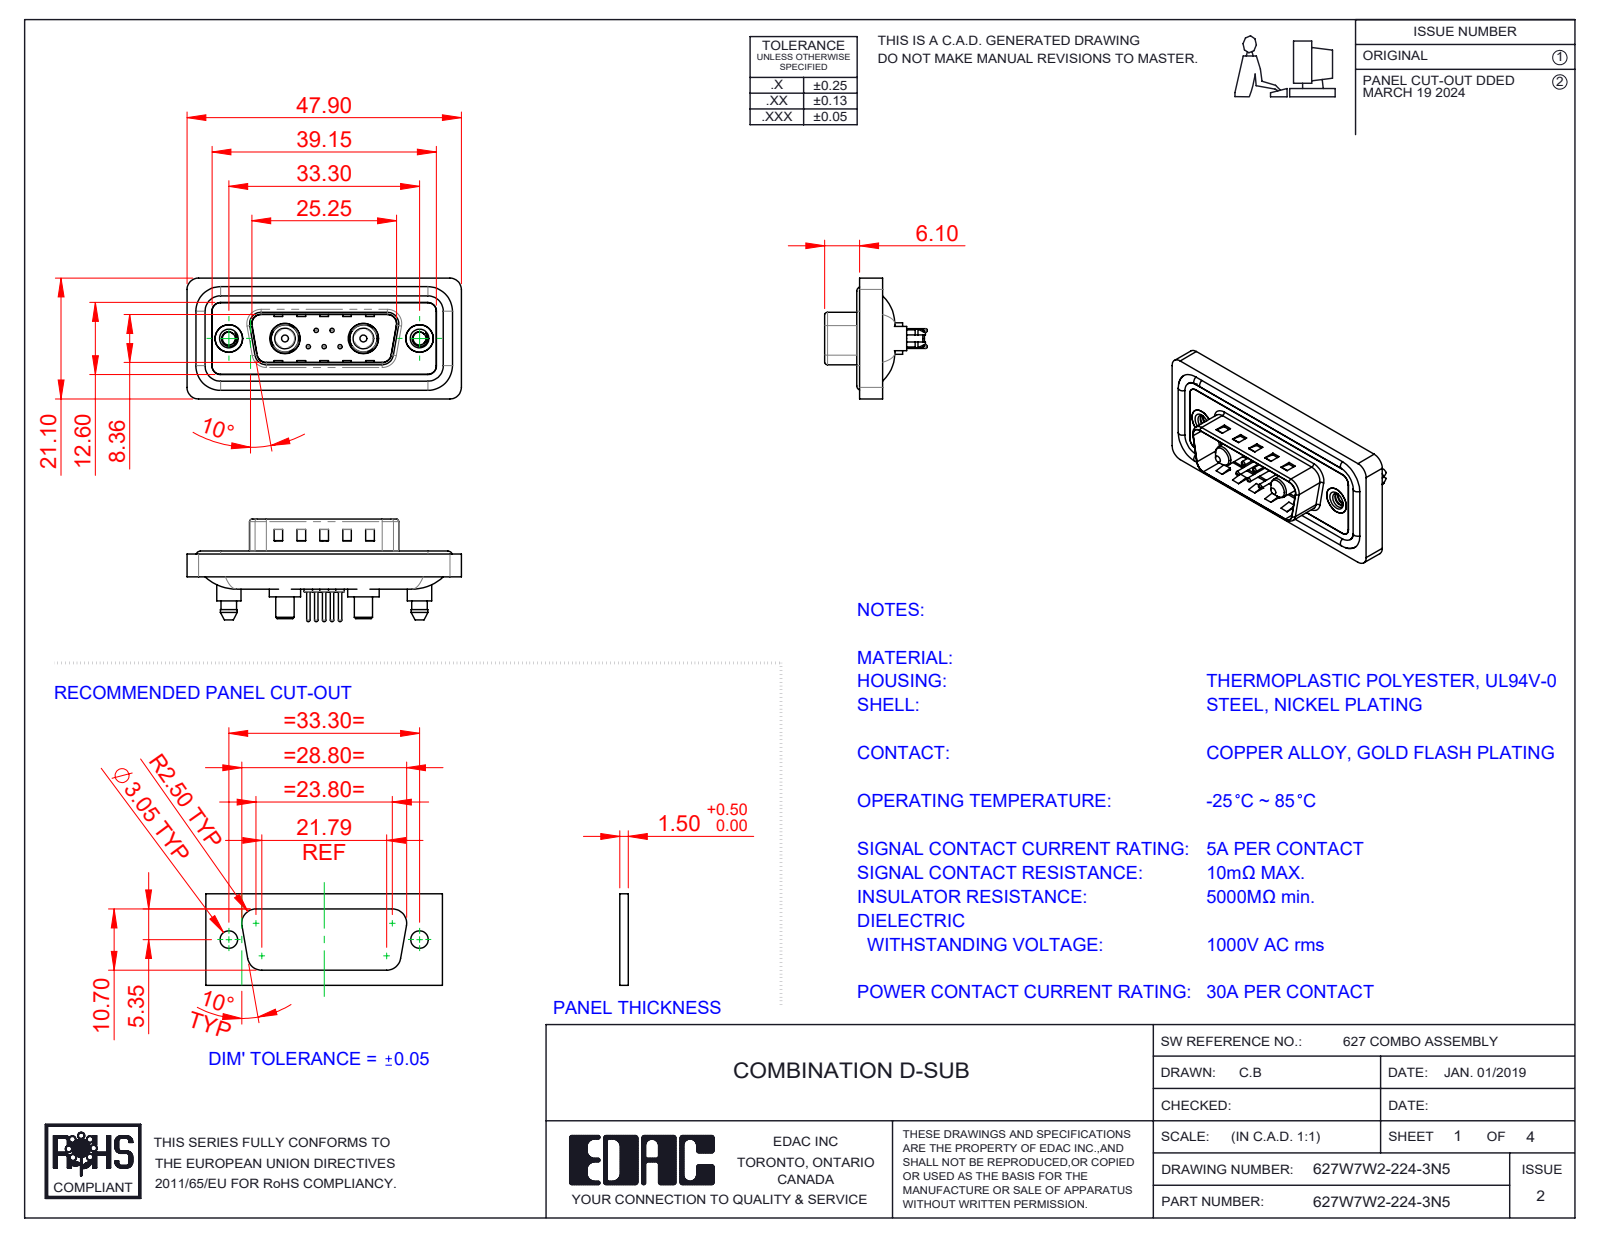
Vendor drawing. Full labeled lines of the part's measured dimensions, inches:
Part name (STEP PRODUCT): 627Combo Contact Row 2_24; 627Combo Waterproof Housing_15 Contacts; 627Combo Shell Rear_15 Contacts; 627Combo Threaded Boardlock_5 (+5 more)
STEP written by: SolidWorks 2023 (CONFIG_CONTROL_DESIGN)
Units: inches
Bodies: 16 solids, 760 faces (248 planar, 324 cylindrical, 188 other)
Overall size (bounding box): 1.886 × 0.831 × 0.705
Volume: 0.346 in³ · Surface area: 14.16 in²
Round holes (diameter × count): ⌀0.03 ×5, ⌀0.063 ×5, ⌀0.079 ×5, ⌀0.089 ×2, ⌀0.157 ×2, ⌀0.189 ×2, ⌀0.191 ×2, ⌀0.197 ×2, ⌀0.209 ×2
Round bosses / shafts (diameter × count): ⌀0.059 ×5, ⌀0.024 ×5, ⌀0.063 ×4, ⌀0.217 ×2, ⌀0.213 ×2, ⌀0.205 ×2, ⌀0.193 ×2, ⌀0.187 ×2
Partial cylindrical surfaces — rounded edges, fillets, slot ends (radius × count): R0.059 ×28, R0.079 ×20, R0.063 ×10, R0.02 ×8, R0.01 ×4, R0.024 ×4, R0.026 ×4, R0.035 ×4
Main face-to-face distances: 0.016, 0.043, 0.059, 0.063, 0.02, 0.122, 0.114, 0.028, 0.157, 0.032
Hole centre spacings: 0.124, 0.109, 0.386, 0.925, 0.17, 0.17, 0.198, 0.198
